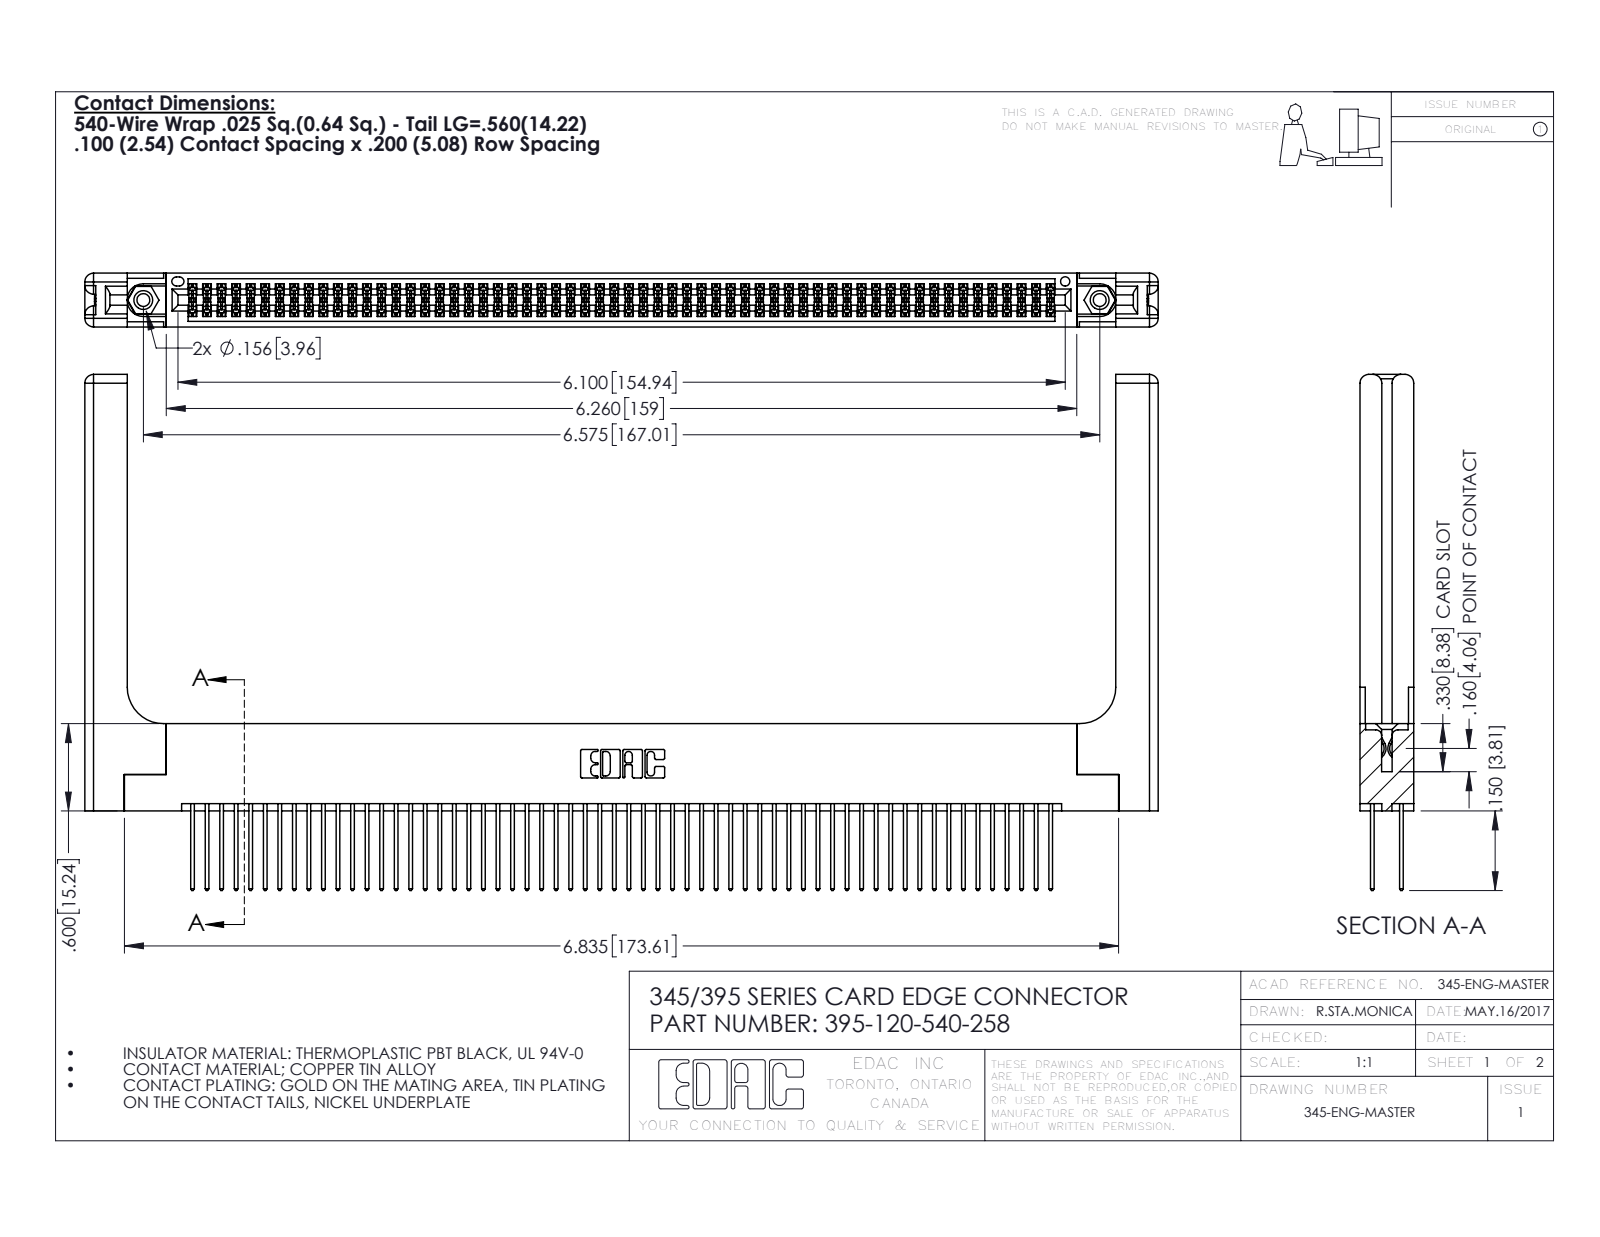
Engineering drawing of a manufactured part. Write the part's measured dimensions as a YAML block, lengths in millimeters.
part_name: "395-120-540-258; 345-250-001_345-250-001-102; 345-292-001_345-293-140; 345-220-058_345-220-058 (+1 more)"
step_written_by: "SolidWorks 2016 (CONFIG_CONTROL_DESIGN)"
units: millimeters
bodies: {solids: 125, faces: 6382, planar: 4188, cylindrical: 2134, other: 60}
overall_size: [187.4, 90.1, 9.4]
volume: 27300
surface_area: 35350
round_holes:
  - {diameter: 2.3, count: 2}
  - {diameter: 3.2, count: 2}
  - {diameter: 4, count: 2}
  - {diameter: 1.6, count: 1}
round_bosses_or_shafts:
  - {diameter: 3.9, count: 2}
partial_cylinders:
  - {radius: 0.2, count: 180}
  - {radius: 0.3, count: 120}
  - {radius: 0.3, count: 22}
  - {radius: 1.5, count: 16}
  - {radius: 0.2, count: 6}
  - {radius: 0.8, count: 6}
  - {radius: 0.7, count: 3}
  - {radius: 0.4, count: 2}
face_to_face_distances: [1.8, 7.6, 5.1, 9.4, 2.5, 6.9, 0.6, 5.7, 4.4, 3.8]
hole_center_spacings: [6.9, 161, 167]
